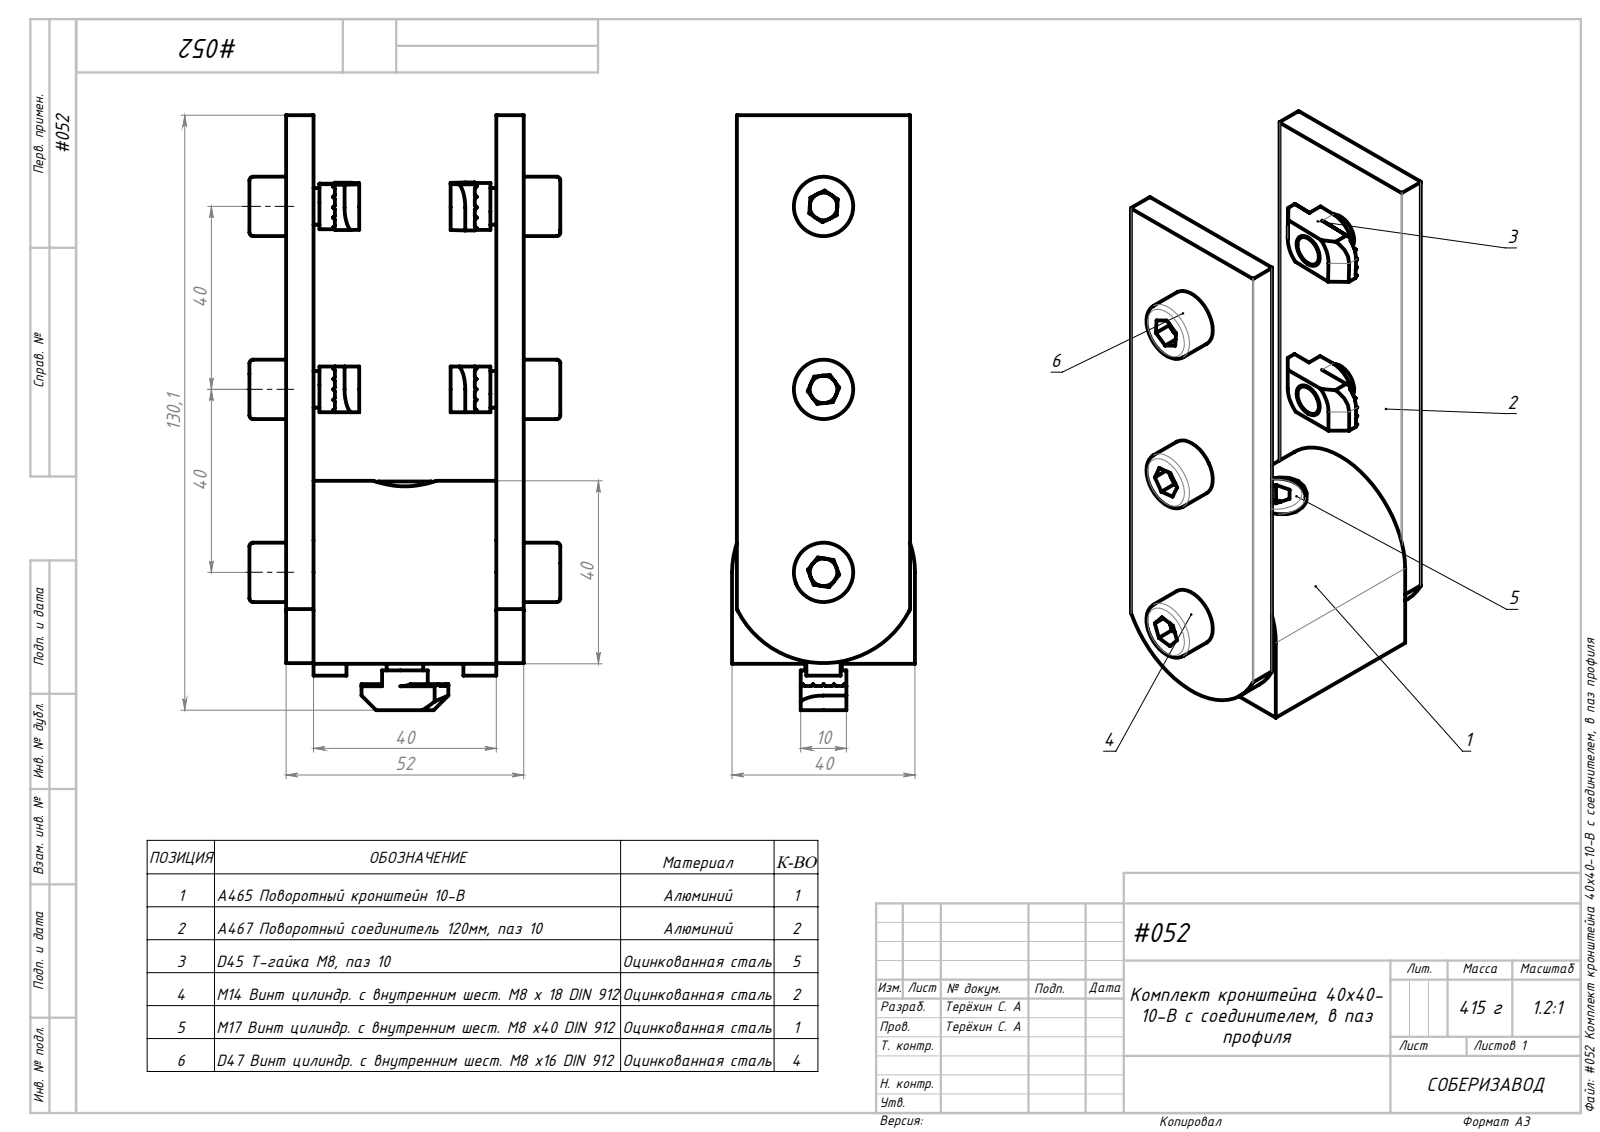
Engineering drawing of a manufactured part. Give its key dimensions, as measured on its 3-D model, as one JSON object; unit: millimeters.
{"part_name": "M17 Винт цилиндр. с внутренним шест. М8 х40 DIN 912; A465 Поворотный кронштейн 10-B; M14 Винт цилиндр. с внутренним шест. М8 х 18 DIN 912; D47 Винт цилиндр. с внутренним шест. М8 х16 DIN 912 (+3 more)", "step_written_by": "SolidWorks 2021 (AUTOMOTIVE_DESIGN)", "units": "millimeters", "bodies": {"solids": 15, "faces": 510, "planar": 319, "cylindrical": 89, "other": 102}, "overall_size": [130.1, 68, 40], "volume_mm3": 121938, "surface_area_mm2": 43998, "round_holes": [[8.5, 4], [6.7, 3], [6.5, 1], [13.7, 1]], "round_bosses_or_shafts": [[13, 4], [8, 4]], "partial_cylinders_radius": [[6, 10], [0.2, 8], [5.67, 6], [20, 1], [21.12, 1]], "face_to_face_distances": [46, 6, 40, 52, 1.05, 38.95, 37.9, 10, 8, 16], "hole_center_spacings": [40, 80]}
